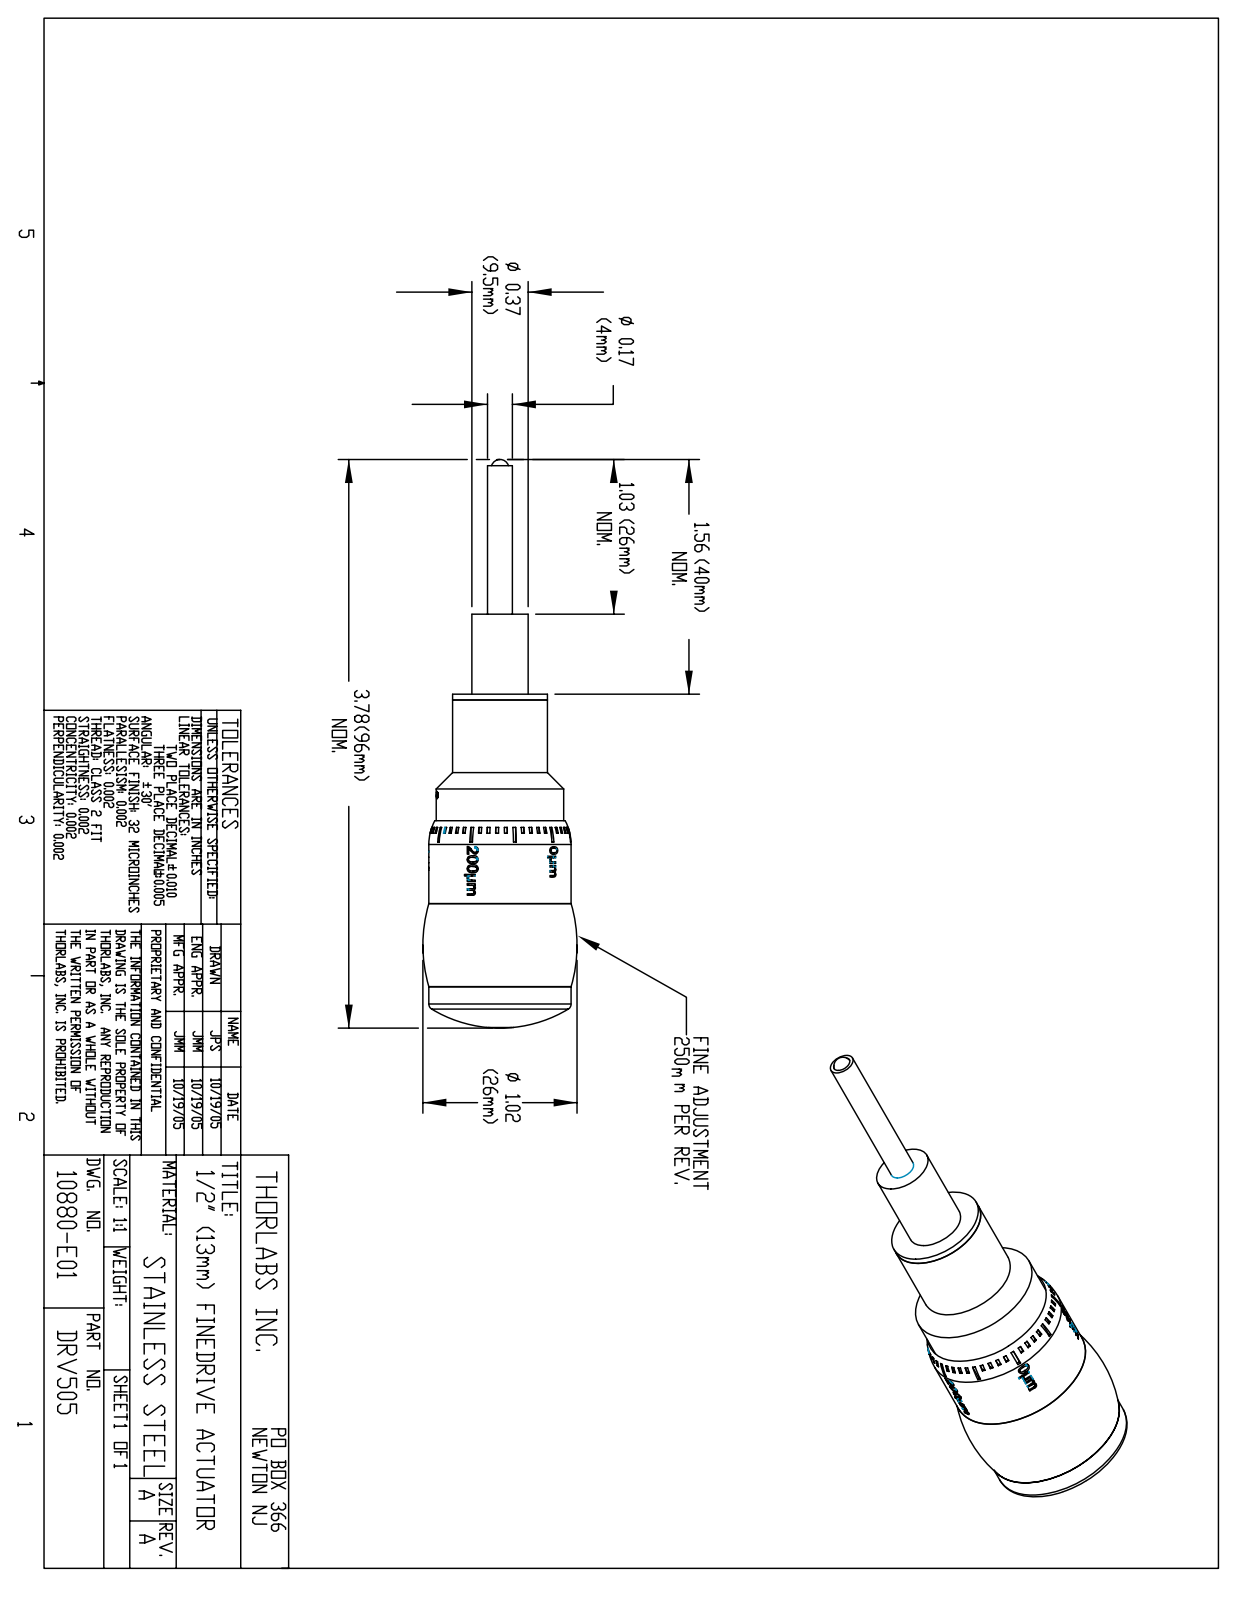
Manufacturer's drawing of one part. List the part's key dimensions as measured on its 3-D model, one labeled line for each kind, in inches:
Part name (STEP PRODUCT): 10880-E0W
STEP written by: SolidWorks 2007 (AUTOMOTIVE_DESIGN)
Units: inches
Bodies: 0 solids, 554 faces (262 planar, 100 cylindrical, 192 other)
Overall size (bounding box): 3.778 × 1.024 × 1.024
Round holes (diameter × count): ⌀0.098 ×1, ⌀0.118 ×1, ⌀0.866 ×1
Round bosses / shafts (diameter × count): ⌀0.945 ×1, ⌀0.846 ×1, ⌀0.63 ×1, ⌀0.374 ×1, ⌀0.165 ×1
Partial cylindrical surfaces — rounded edges, fillets, slot ends (radius × count): R0.404 ×1, R0.453 ×1
Main face-to-face distances: 0.531, 0.039, 0.571, 2.176, 2.215, 2.746, 3.733, 1.557, 1.518, 0.986
